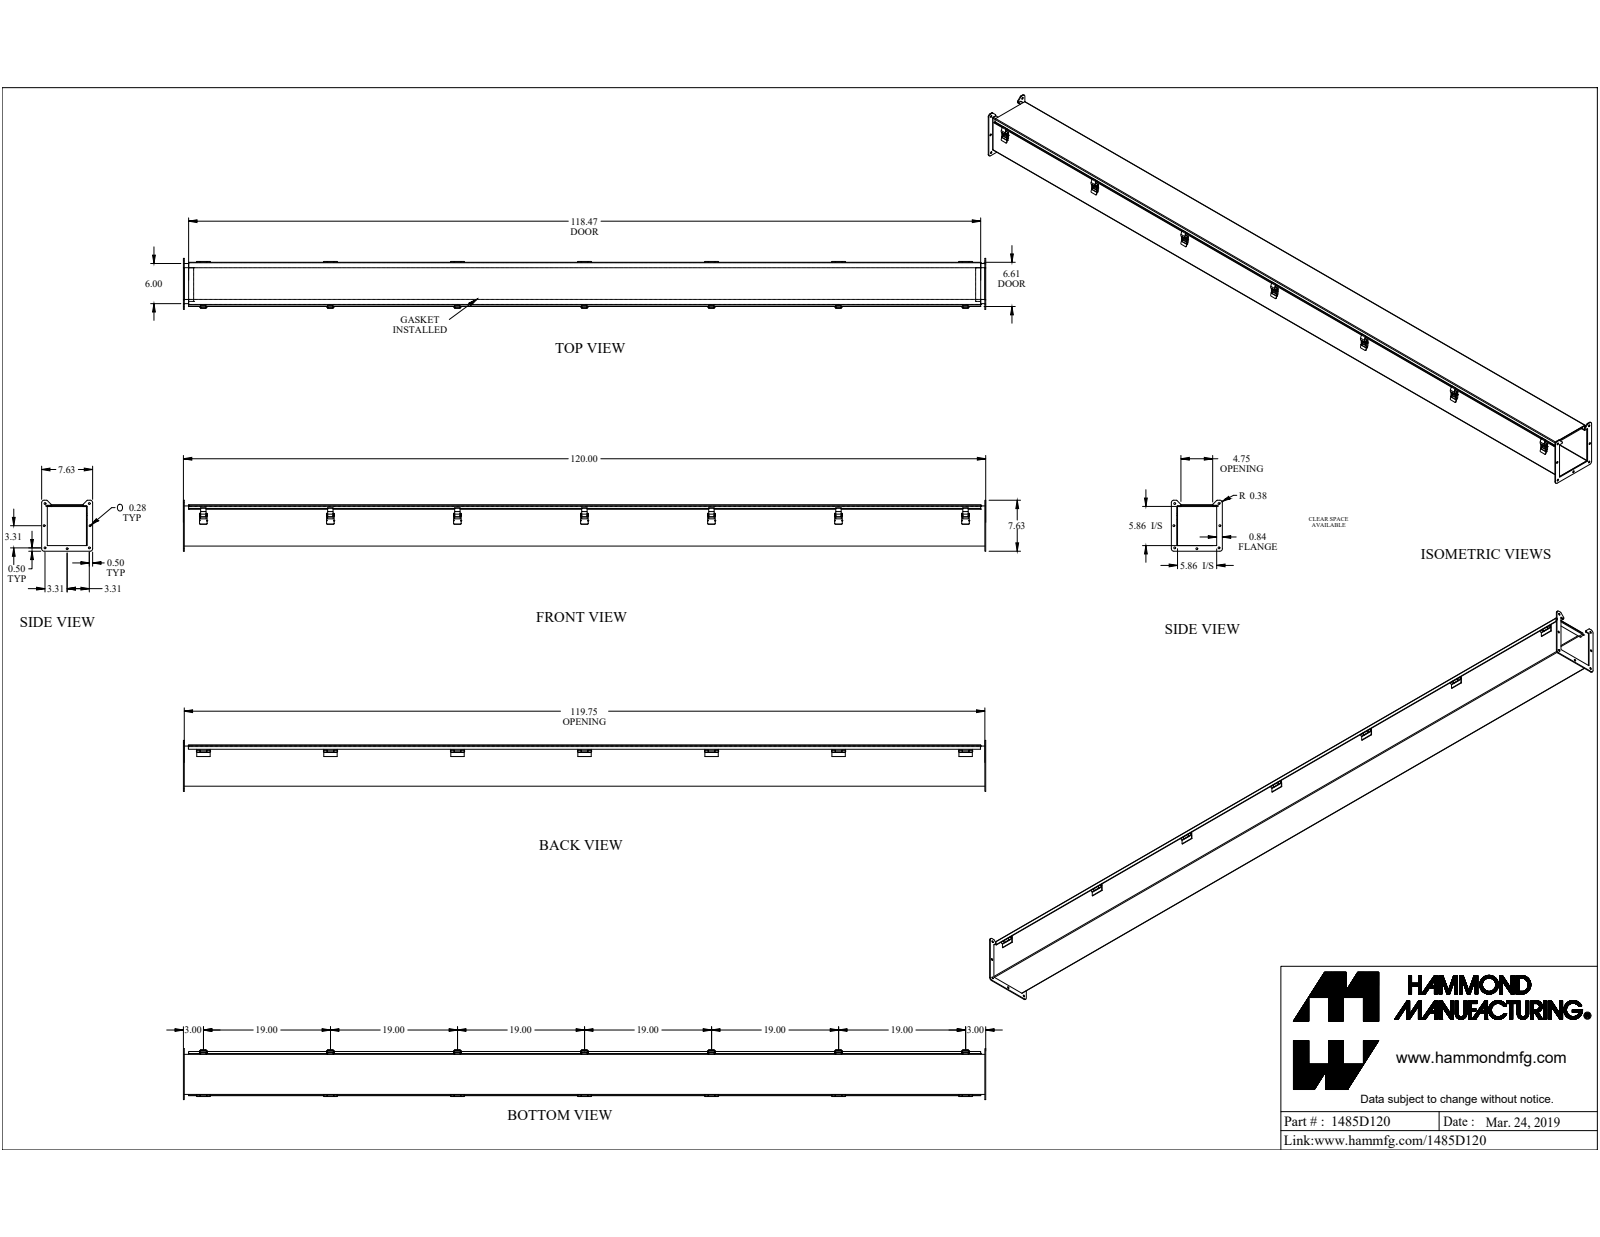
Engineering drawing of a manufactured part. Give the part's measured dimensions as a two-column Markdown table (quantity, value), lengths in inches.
| quantity | value |
| --- | --- |
| part name | 1485D120 |
| STEP written by | SolidWorks 2019 (CONFIG_CONTROL_DESIGN) |
| units | inches |
| bodies | 50 solids, 1141 faces (670 planar, 457 cylindrical, 14 other) |
| overall size | 120 × 7.625 × 7.625 |
| volume | 271.1 in³ |
| surface area | 7 059 in² |
| round holes (diameter × count) | 0.281 × 7, 0.125 × 1, 0.13 × 1, 0.164 × 1 |
| round bosses / shafts (diameter × count) | 0.187 × 2, 0.275 × 1, 0.156 × 1, 0.125 × 1, 0.125 × 1 |
| partial cylindrical surfaces (radius × count) | 0.016 × 43, 0.125 × 19, 0.035 × 15, 0.039 × 15, 0.076 × 15, 0.015 × 14, 0.029 × 14, 0.086 × 14 |
| main face-to-face distances | 0.072, 5.928, 6.1, 6, 5.856, 6.028, 6.172, 0.172, 5.913, 5.841 |
| hole center spacings | 7.519, 6.625, 3.315, 3.315, 9.369, 0.285, 1.112, 1.459 |
